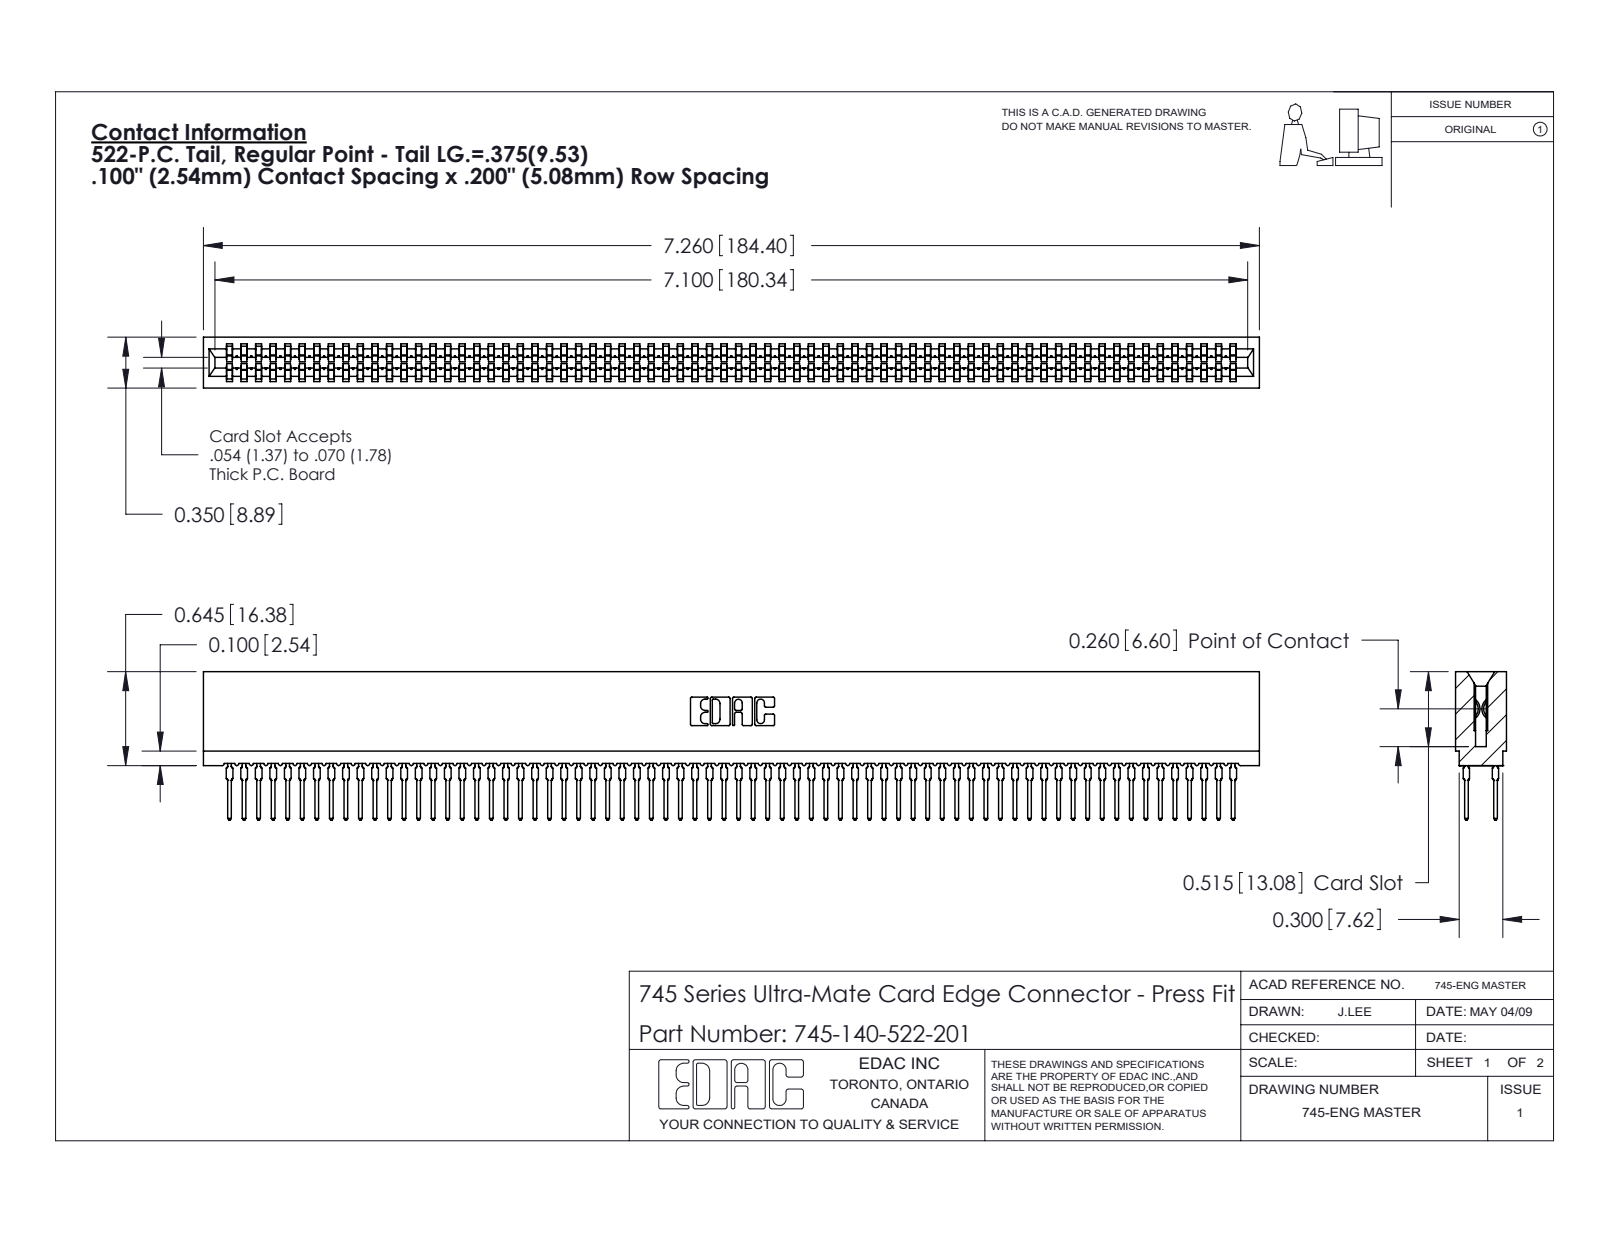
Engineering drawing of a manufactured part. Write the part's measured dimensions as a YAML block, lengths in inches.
part_name: "745 Part_Insulator Option - 01; 745-140-522-201; 745-292-001_522"
step_written_by: "SolidWorks 2020 (CONFIG_CONTROL_DESIGN)"
units: inches
bodies: {solids: 141, faces: 12625, planar: 6495, cylindrical: 2490, other: 3640}
overall_size: [7.26, 1.021, 0.35]
volume: 1.012
surface_area: 54.02
partial_cylinders:
  - {radius: 0.021, count: 280}
  - {radius: 0.015, count: 140}
  - {radius: 0.01, count: 22}
  - {radius: 0.005, count: 8}
  - {radius: 0.011, count: 8}
  - {radius: 0.007, count: 6}
  - {radius: 0.031, count: 6}
  - {radius: 0.026, count: 3}
face_to_face_distances: [0.35, 0.063, 0.287, 0.045, 0.305, 0.018, 0.243, 0.138, 0.212, 0.093]
